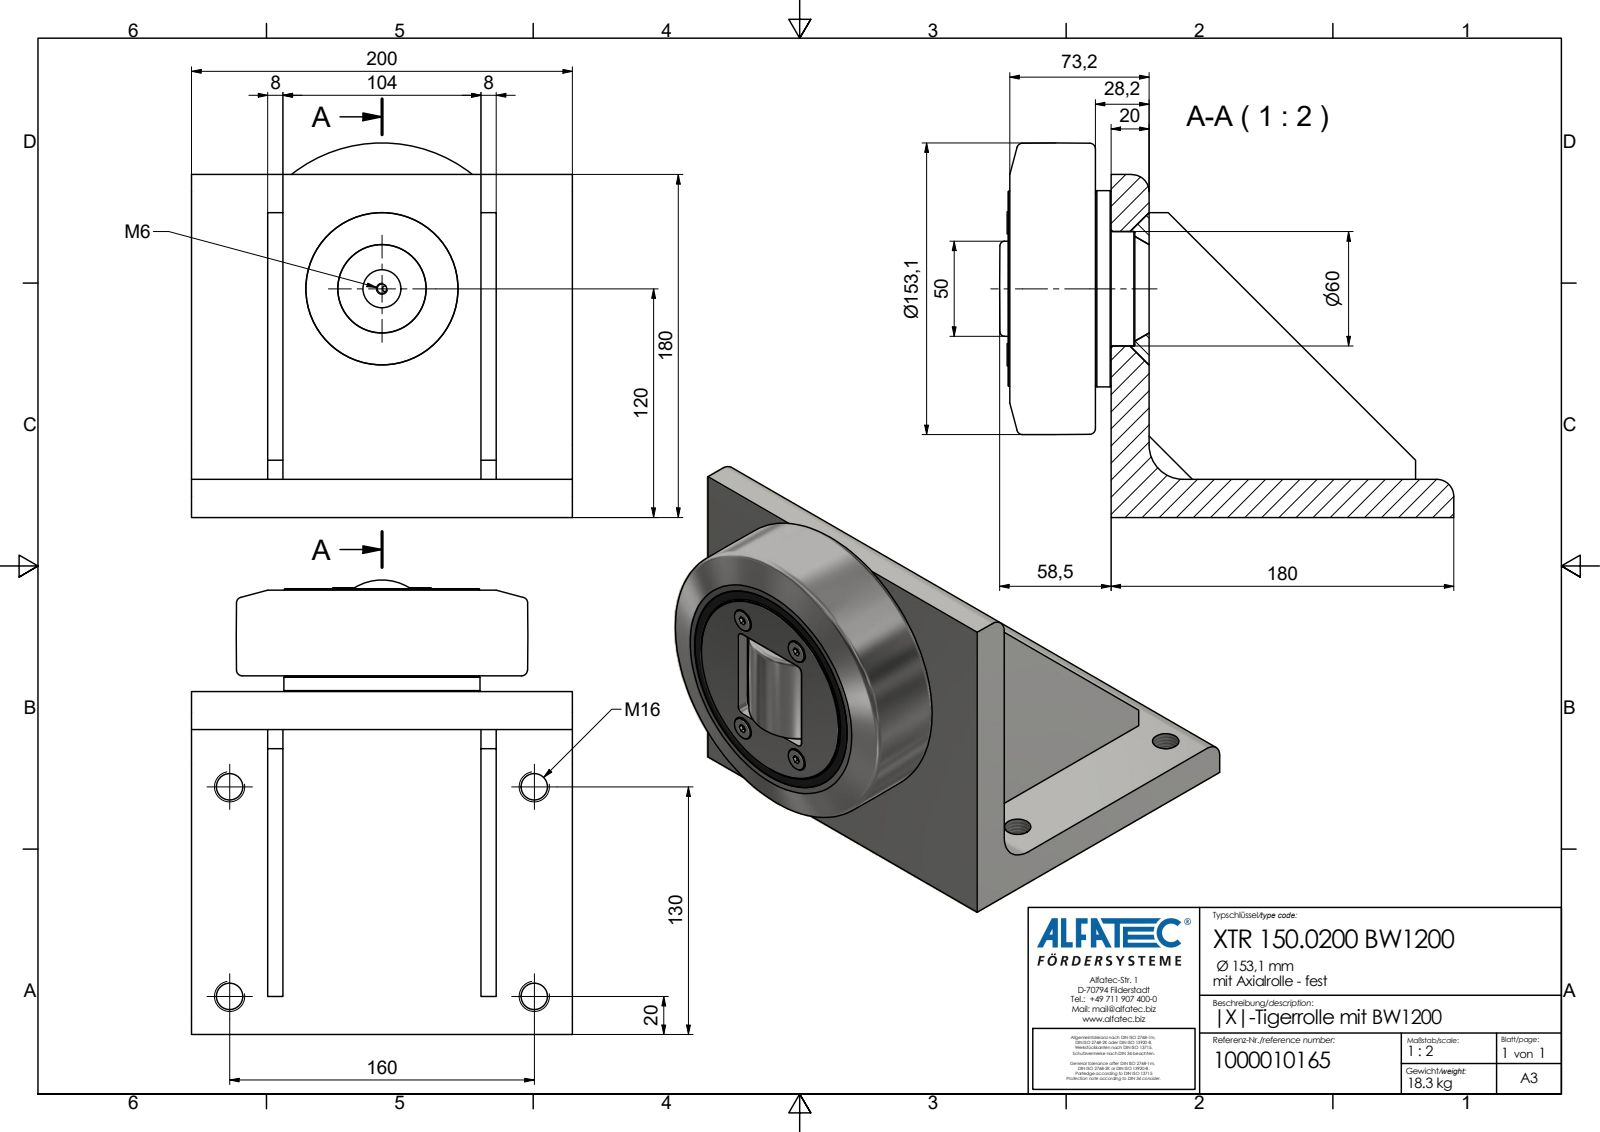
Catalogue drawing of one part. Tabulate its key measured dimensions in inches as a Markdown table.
| quantity | value |
| --- | --- |
| part name | XTR 150.0200 BW1200_Kontur |
| STEP written by | Autodesk Inventor 2020 (AP242_MANAGED_MODEL_BASED_3D_ENGINEERING_MIM_LF) |
| units | inches |
| bodies | 1 solid, 86 faces (58 planar, 14 cylindrical, 14 other) |
| overall size | 9.39 × 7.874 × 7.738 |
| volume | 147.6 in³ |
| surface area | 377 in² |
| round holes (diameter × count) | 0.545 × 4 |
| round bosses / shafts (diameter × count) | 0.461 × 4, 4.055 × 1, 4.035 × 1, 3.992 × 1 |
| partial cylindrical surfaces (radius × count) | 0.354 × 2, 0.709 × 1 |
| main face-to-face distances | 0.787, 0.315, 4.409, 6.299, 1.575, 1.89, 5.984, 4.094, 4.724, 0.323 |
| hole center spacings | 4.331, 6.299, 7.644 |
